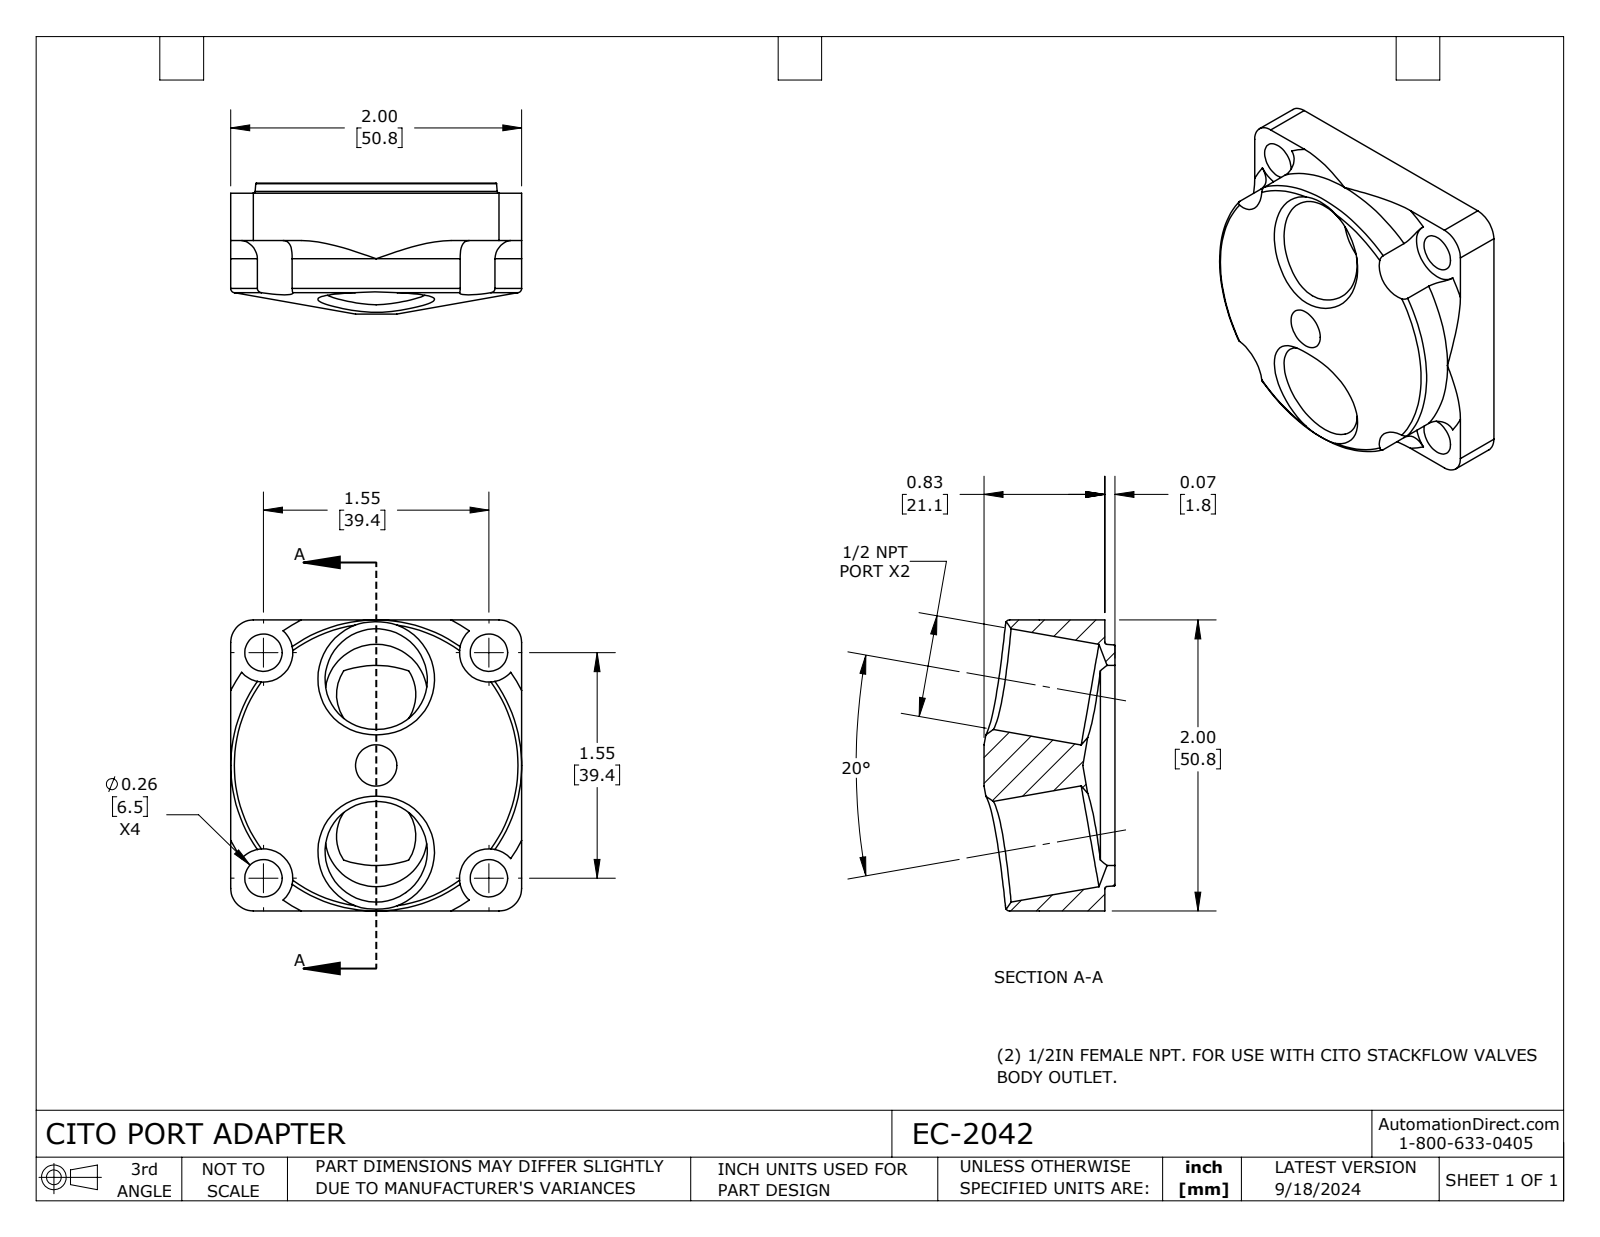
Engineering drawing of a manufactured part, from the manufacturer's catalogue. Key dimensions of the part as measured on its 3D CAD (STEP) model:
Part name (STEP PRODUCT): EC-2042
STEP written by: SolidWorks 2023 (CONFIG_CONTROL_DESIGN)
Units: inches
Bodies: 1 solid, 70 faces (11 planar, 29 cylindrical, 30 other)
Overall size (bounding box): 2 × 2 × 0.9
Volume: 1.901 in³ · Surface area: 15.94 in²
Round holes (diameter × count): ⌀0.257 ×4, ⌀0.703 ×2, ⌀1.375 ×1
Partial cylindrical surfaces — rounded edges, fillets, slot ends (radius × count): R0.156 ×4, R0.202 ×4, R1 ×1
Main face-to-face distances: 2, 0.07, 0.325, 0.395, 0.505, 0.83, 0.9
Hole centre spacings: 1.096, 1.55, 2.191
